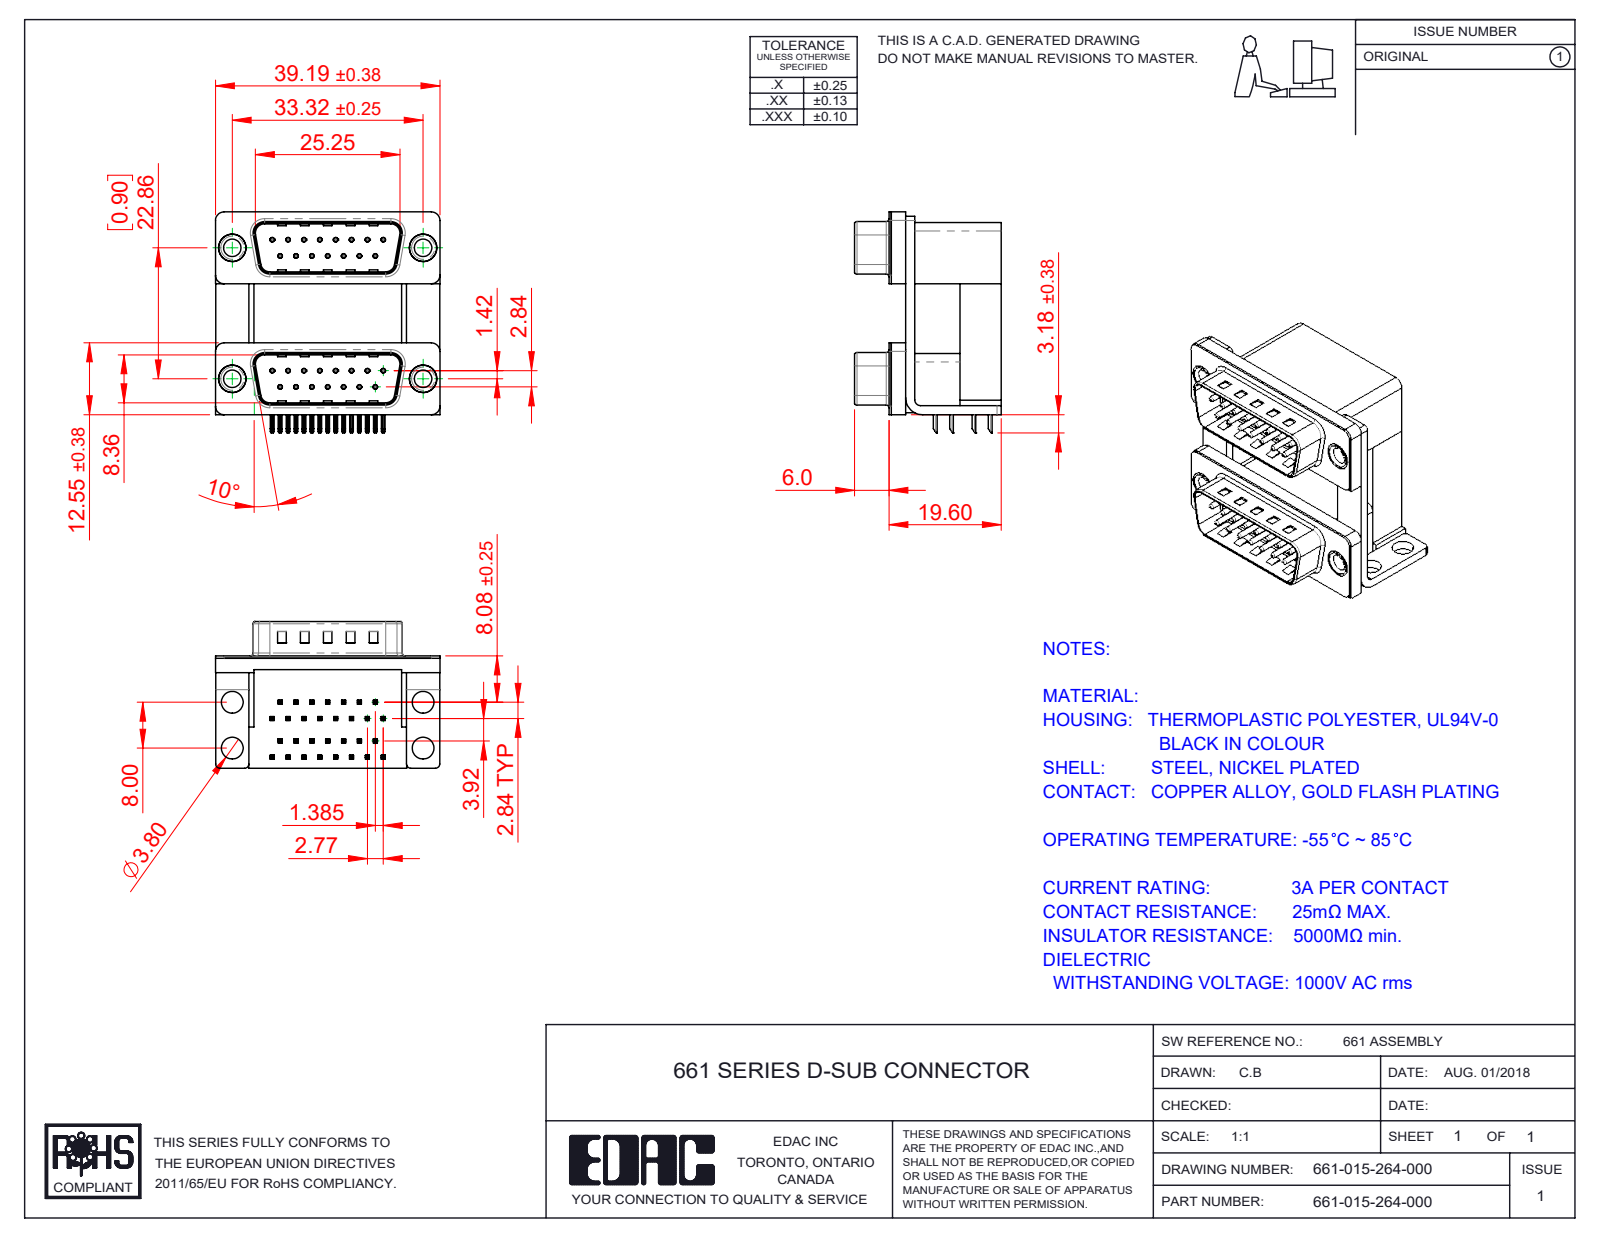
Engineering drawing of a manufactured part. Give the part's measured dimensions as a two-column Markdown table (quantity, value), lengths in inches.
| quantity | value |
| --- | --- |
| part name | 661 Contact Bottom Lower; 661 Housing Spacer_15 Contacts H; 661-015-264-000; 661 Thru Hole Rivet (+7 more) |
| STEP written by | SolidWorks 2020 (CONFIG_CONTROL_DESIGN) |
| units | inches |
| bodies | 41 solids, 2878 faces (1834 planar, 818 cylindrical, 226 other) |
| overall size | 1.543 × 1.519 × 1.008 |
| volume | 0.922 in³ |
| surface area | 25.22 in² |
| round holes (diameter × count) | 0.014 × 30, 0.031 × 30, 0.12 × 4, 0.138 × 4, 0.15 × 4, 0.157 × 4, 0.189 × 4, 0.197 × 4 |
| round bosses / shafts (diameter × count) | 0.03 × 30, 0.193 × 4, 0.187 × 4, 0.152 × 4 |
| partial cylindrical surfaces (radius × count) | 0.01 × 120, 0.005 × 60, 0.02 × 16, 0.059 × 16, 0.03 × 8, 0.035 × 8, 0.063 × 8, 0.079 × 8 |
| main face-to-face distances | 0.016, 0.472, 0.9, 0.756, 0.283, 0.657, 0.374, 0.098, 0.488, 0.063 |
| hole center spacings | 0.124, 0.109, 0.907, 0.218, 0.926, 0.327, 0.957, 0.9 |
